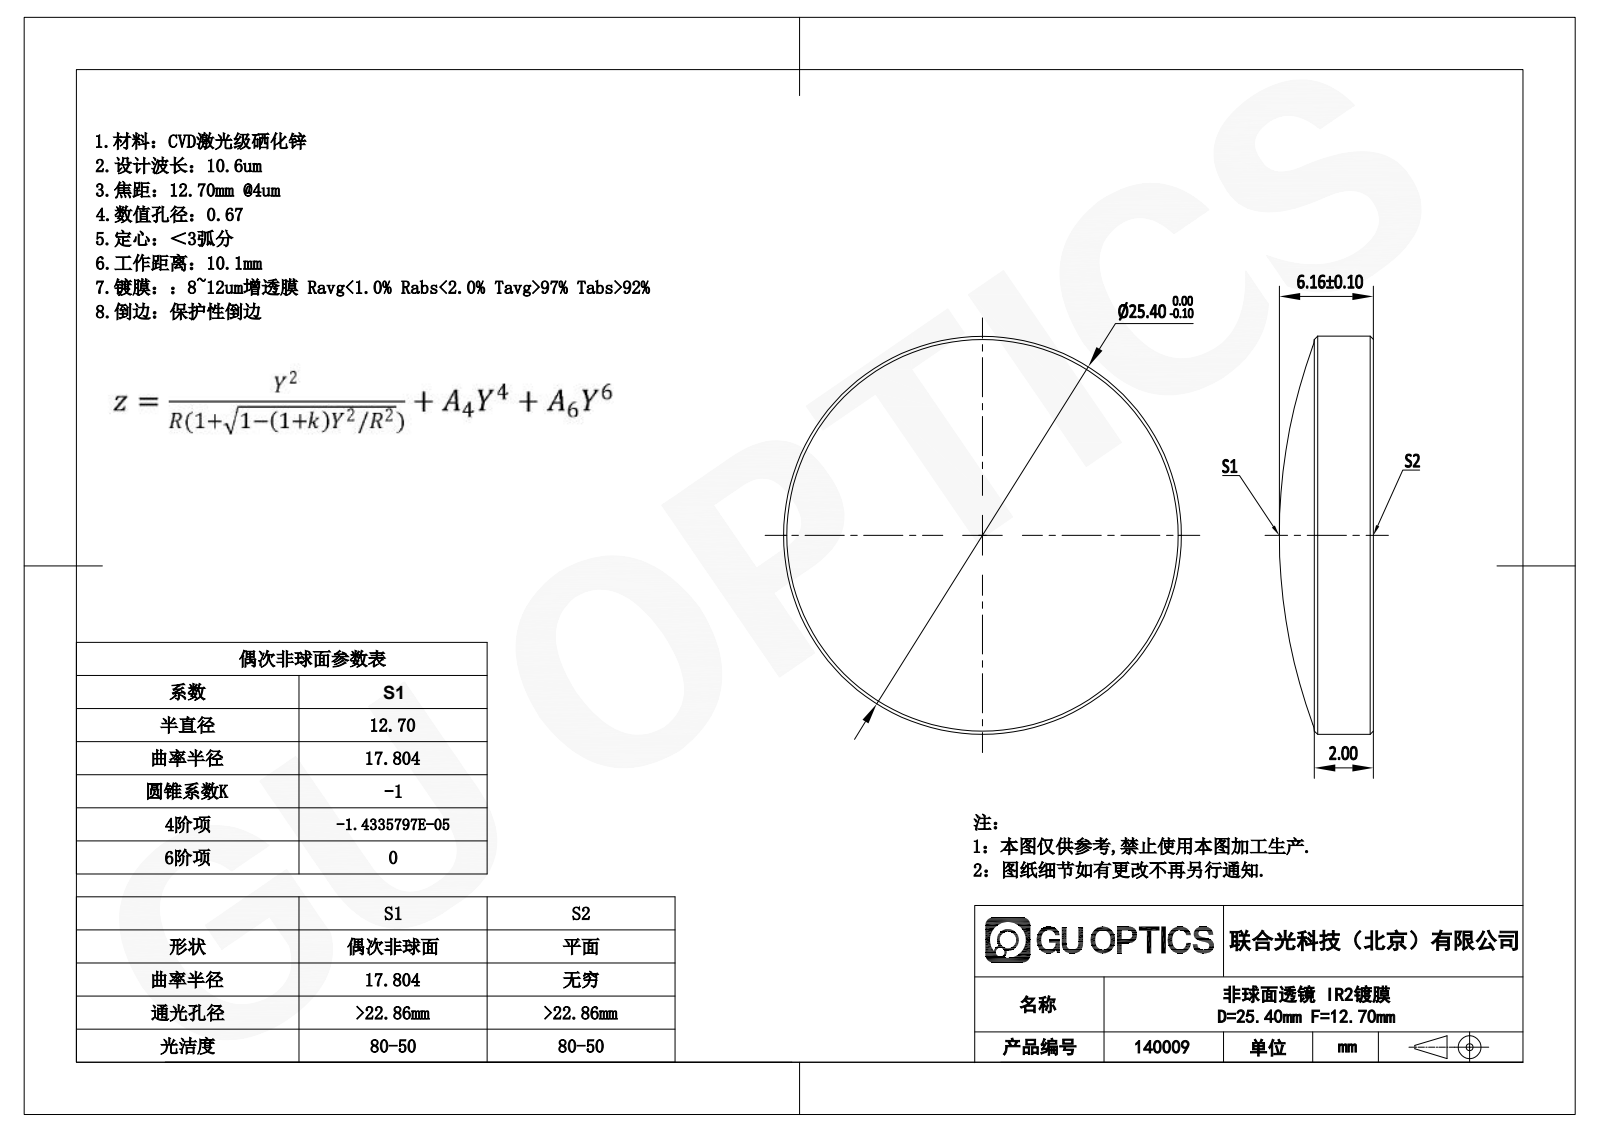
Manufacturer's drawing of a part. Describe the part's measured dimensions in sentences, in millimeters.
The part is named "GL7AL2-025-012-IR2". Its 3-D file was written by "SolidWorks 2022 (AUTOMOTIVE_DESIGN)". It is 1 solid with 11 faces: 1 planar, 2 cylindrical and 8 other. Overall it measures 25.4 by 25.4 by 6.16 millimeters. Its volume is 1 914 cubic millimeters and its surface area 1 202 square millimeters. Round bosses or shafts: 1 of diameter 25.4.
